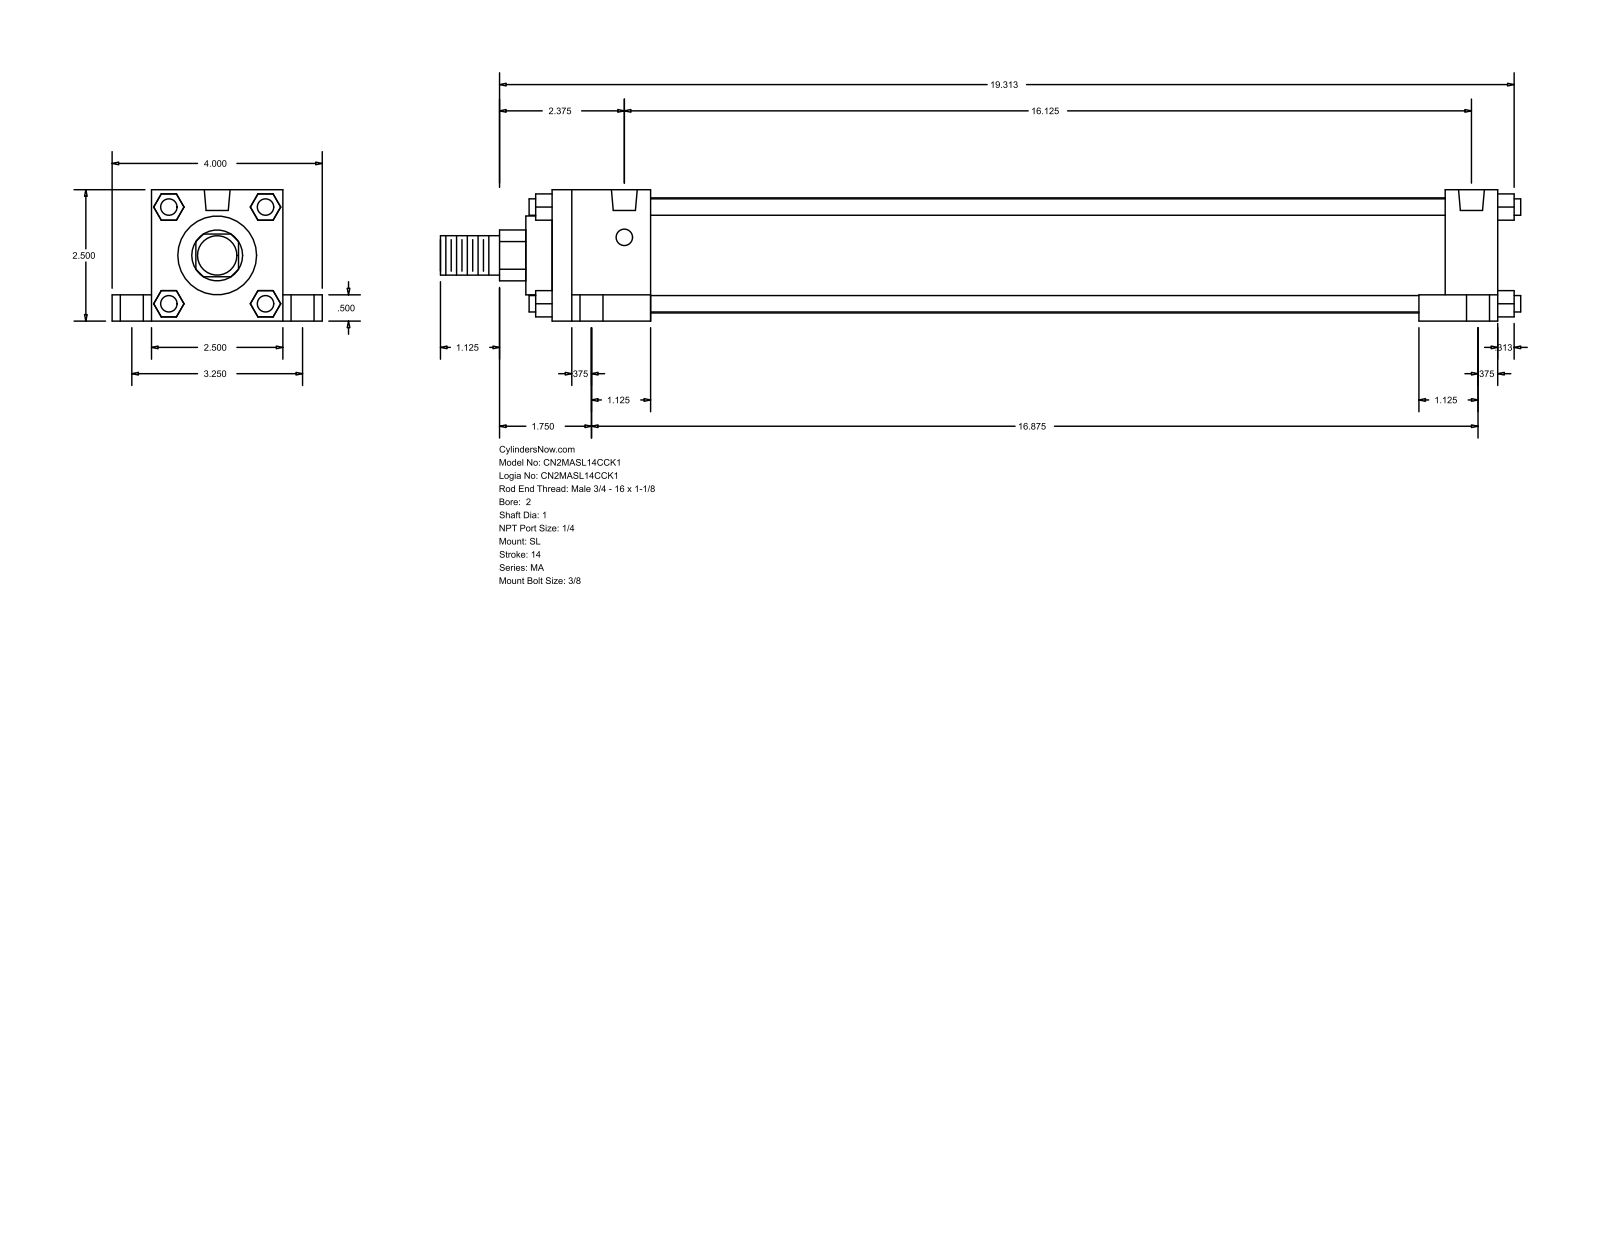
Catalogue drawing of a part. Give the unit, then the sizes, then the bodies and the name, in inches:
Units: inches
Overall size (bounding box): 20.563 × 4 × 2.5
Round holes (diameter × count): ⌀0.313 ×4, ⌀0.437 ×4, ⌀0.687 ×4, ⌀0.492 ×2
Round bosses / shafts (diameter × count): ⌀0.313 ×4, ⌀2.19 ×1, ⌀1.5 ×1, ⌀1 ×1, ⌀0.75 ×1
Partial cylindrical surfaces — rounded edges, fillets, slot ends (radius × count): R0.484 ×1
Main face-to-face distances: 2.5, 0.5, 18, 0.75, 3.25, 1, 2, 1.875, 16.125, 17
Hole centre spacings: 1.63, 1.741, 3.25, 16.125, 16.331, 16.829, 16.875, 17.185
Bodies: 0 solids, 148 faces (112 planar, 36 cylindrical, 0 other)
Part name (STEP PRODUCT): MA_SL__0200_1
STEP written by: GSSL Pune (CONFIG_CONTROL_DESIGN)
